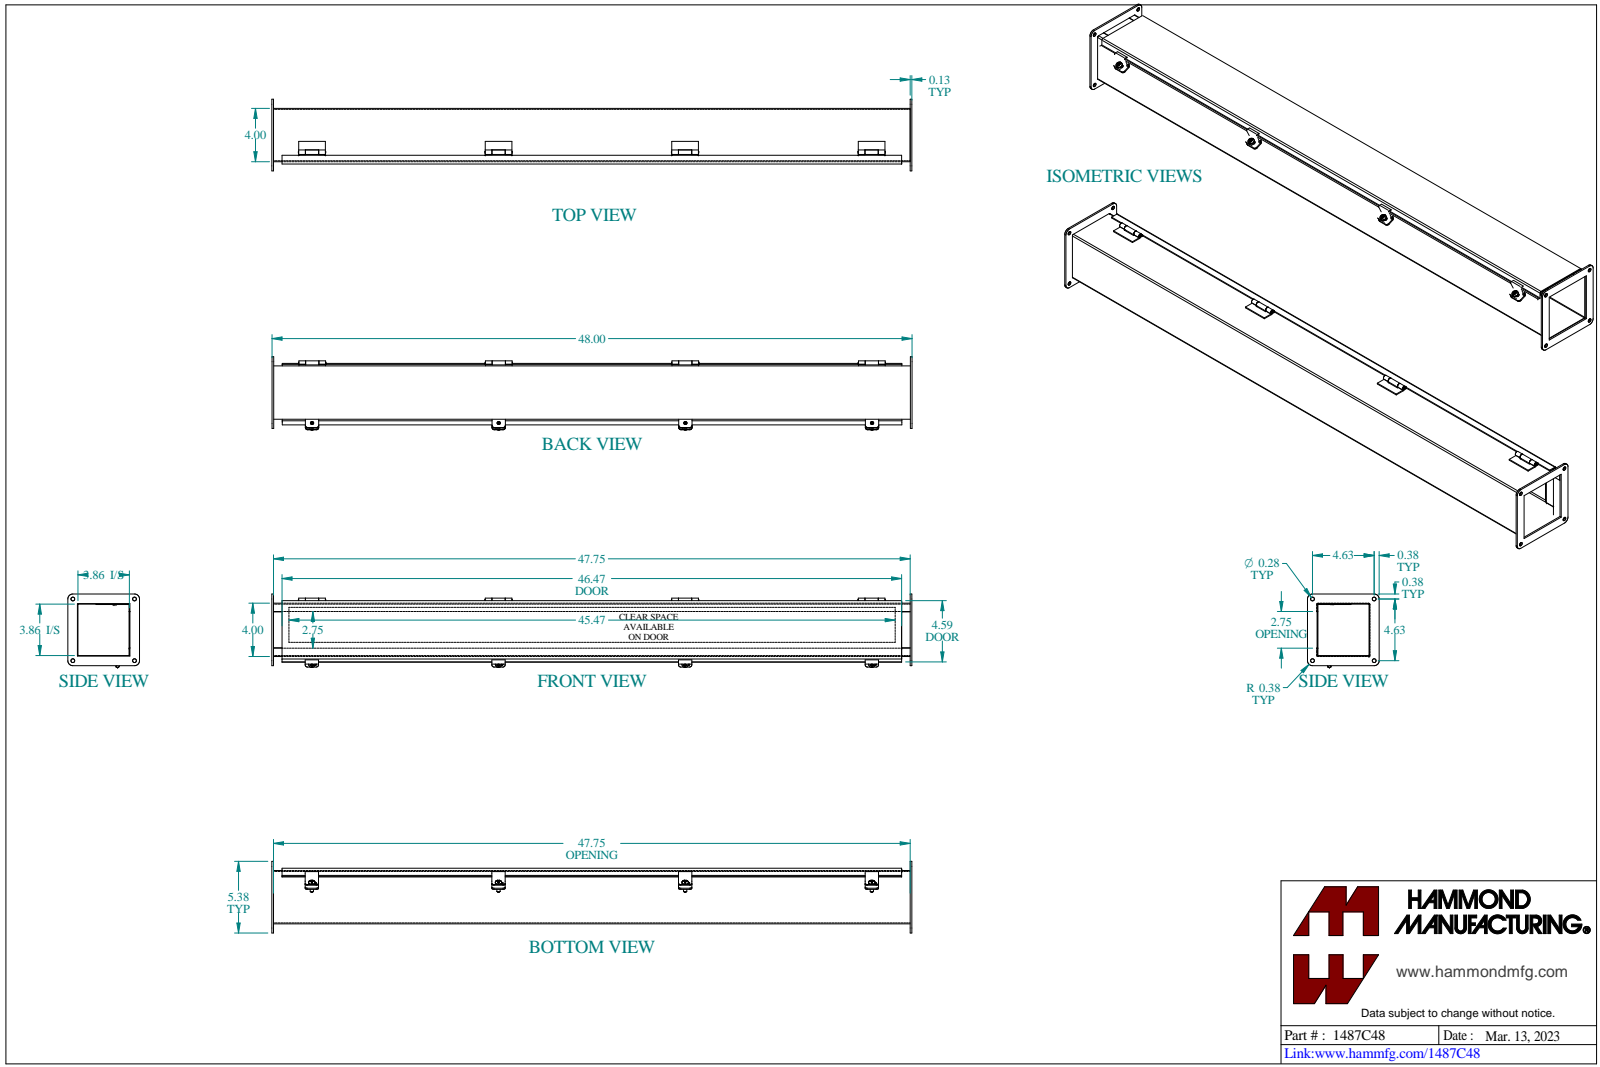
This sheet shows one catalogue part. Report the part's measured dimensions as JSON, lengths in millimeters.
{"part_name": "1487C48", "step_written_by": "SolidWorks 2023 (CONFIG_CONTROL_DESIGN)", "units": "millimeters", "bodies": {"solids": 31, "faces": 682, "planar": 376, "cylindrical": 230, "other": 76}, "overall_size": [1222.4, 139.8, 136.5], "volume_mm3": 1162000, "surface_area_mm2": 1257000, "round_holes": [[7.1, 8], [5.4, 4], [3.2, 1]], "round_bosses_or_shafts": [[12.2, 4], [6.2, 4], [7, 1]], "partial_cylinders_radius": [[4.8, 16], [0.3, 8], [3.6, 8], [0.9, 7], [2.7, 7], [6.4, 4], [9.5, 4], [0.7, 2]], "face_to_face_distances": [1.8, 99.8, 104.1, 101.6, 97.9, 102.3, 106, 4.4, 2.5, 6.2], "hole_center_spacings": [117.5, 58.7, 58.8, 131.3, 131.3, 83.1, 355.6, 166.1]}
